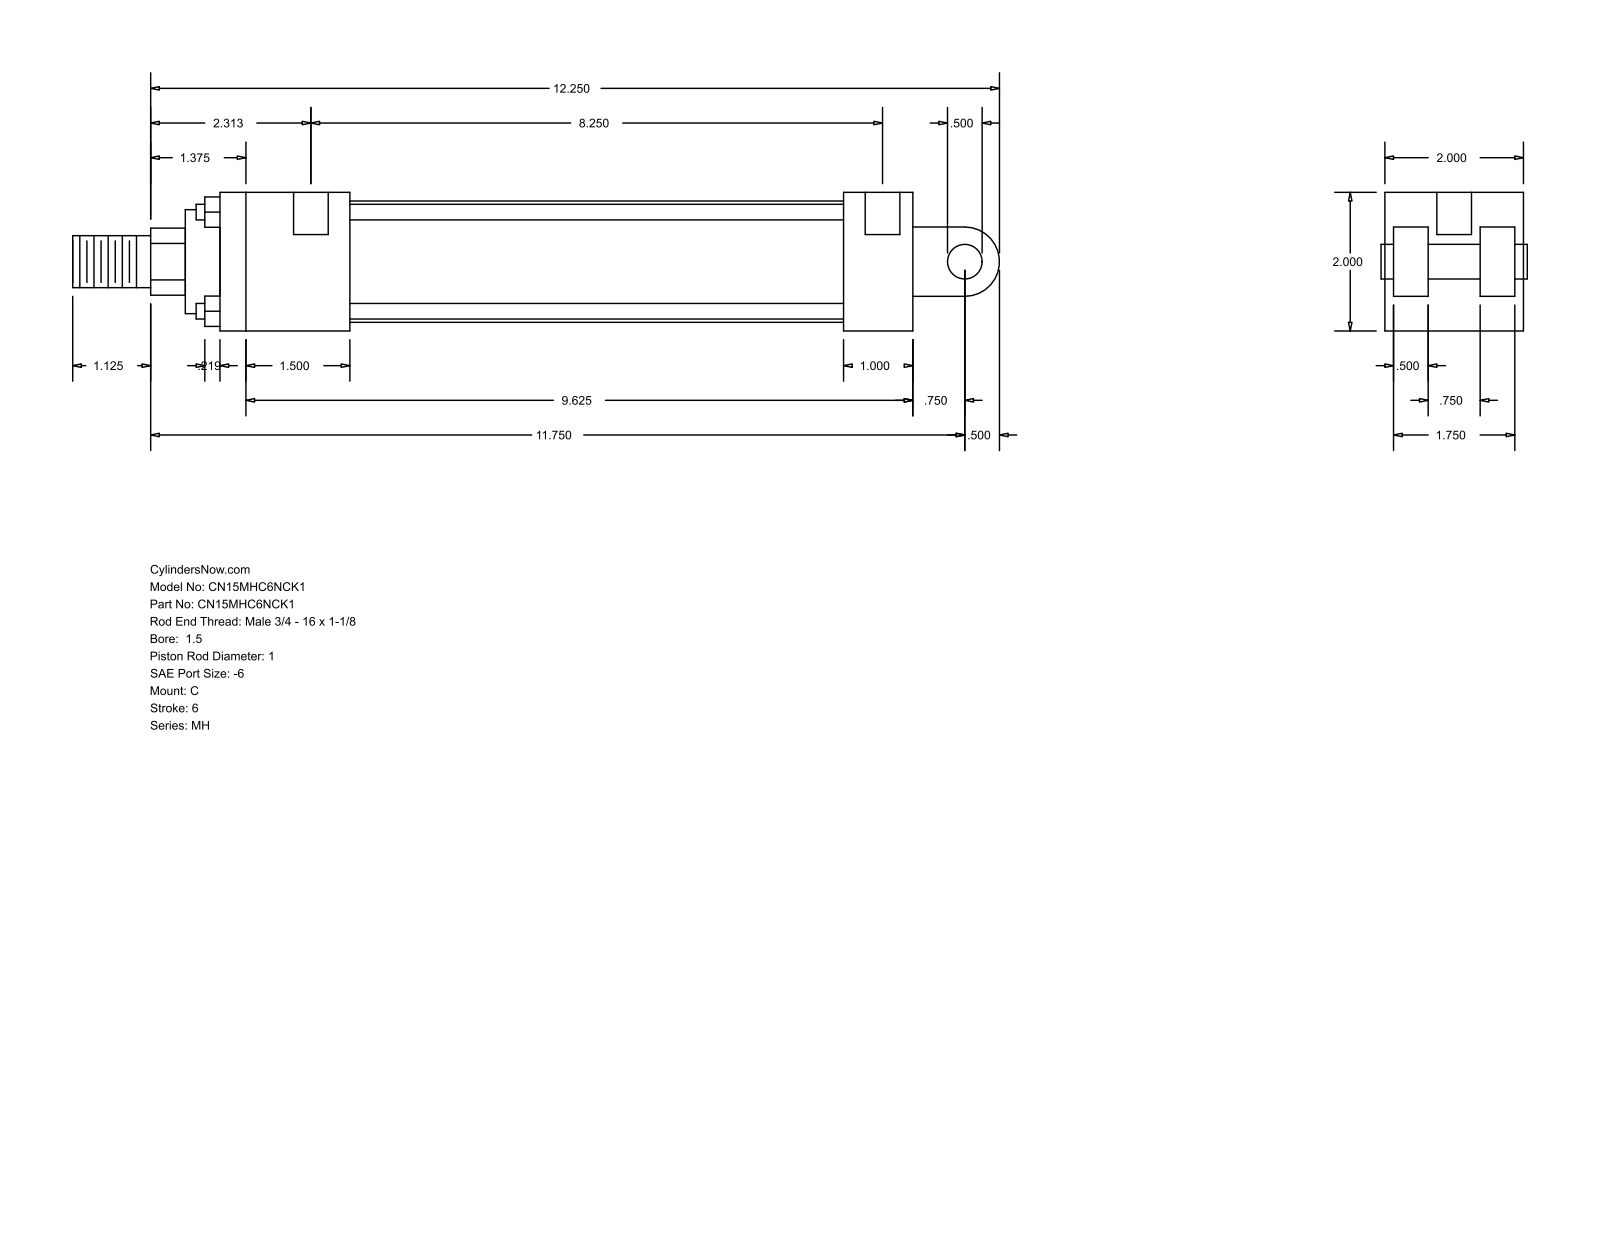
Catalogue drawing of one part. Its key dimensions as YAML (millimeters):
part_name: "MH_C__0150_1"
step_written_by: "GSSL Pune (CONFIG_CONTROL_DESIGN)"
units: millimeters
bodies: {solids: 0, faces: 99, planar: 70, cylindrical: 29, other: 0}
overall_size: [339.73, 50.8, 50.8]
round_holes:
  - {diameter: 5.56, count: 4}
  - {diameter: 12.7, count: 2}
round_bosses_or_shafts:
  - {diameter: 5.71, count: 4}
  - {diameter: 44.45, count: 1}
  - {diameter: 38.1, count: 1}
  - {diameter: 25.4, count: 1}
  - {diameter: 19.05, count: 1}
  - {diameter: 12.7, count: 1}
partial_cylinders:
  - {radius: 12.29, count: 1}
  - {radius: 12.7, count: 1}
face_to_face_distances: [50.8, 12.7, 47.63, 25.4, 3.17, 15.87, 34.93, 31.76, 254, 38.1]
hole_center_spacings: [212.73, 3.18, 209.55]
